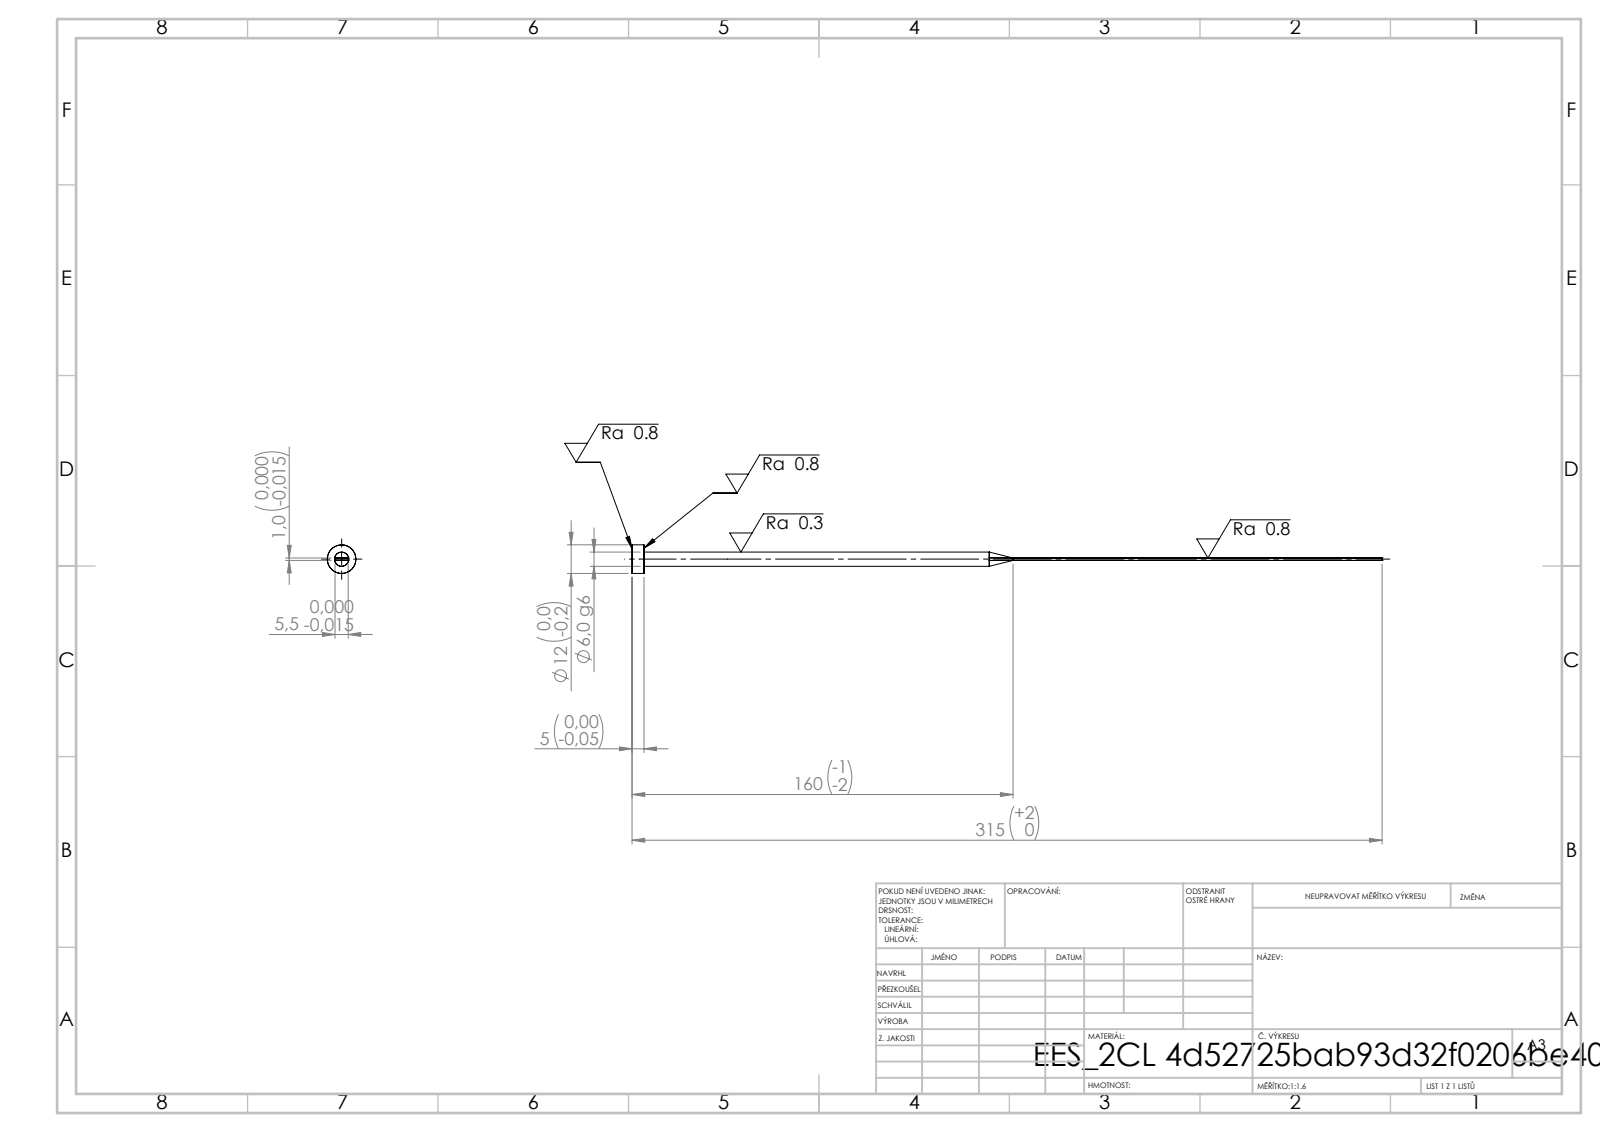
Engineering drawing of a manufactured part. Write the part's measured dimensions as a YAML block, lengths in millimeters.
step_written_by: "SolidWorks 2019 (CONFIG_CONTROL_DESIGN)"
units: millimeters
bodies: {solids: 1, faces: 15, planar: 7, cylindrical: 4, other: 4}
overall_size: [315, 12, 12]
volume: 5677
surface_area: 5294
round_bosses_or_shafts:
  - {diameter: 12, count: 1}
  - {diameter: 6, count: 1}
face_to_face_distances: [1, 5.5, 5, 315, 310]
